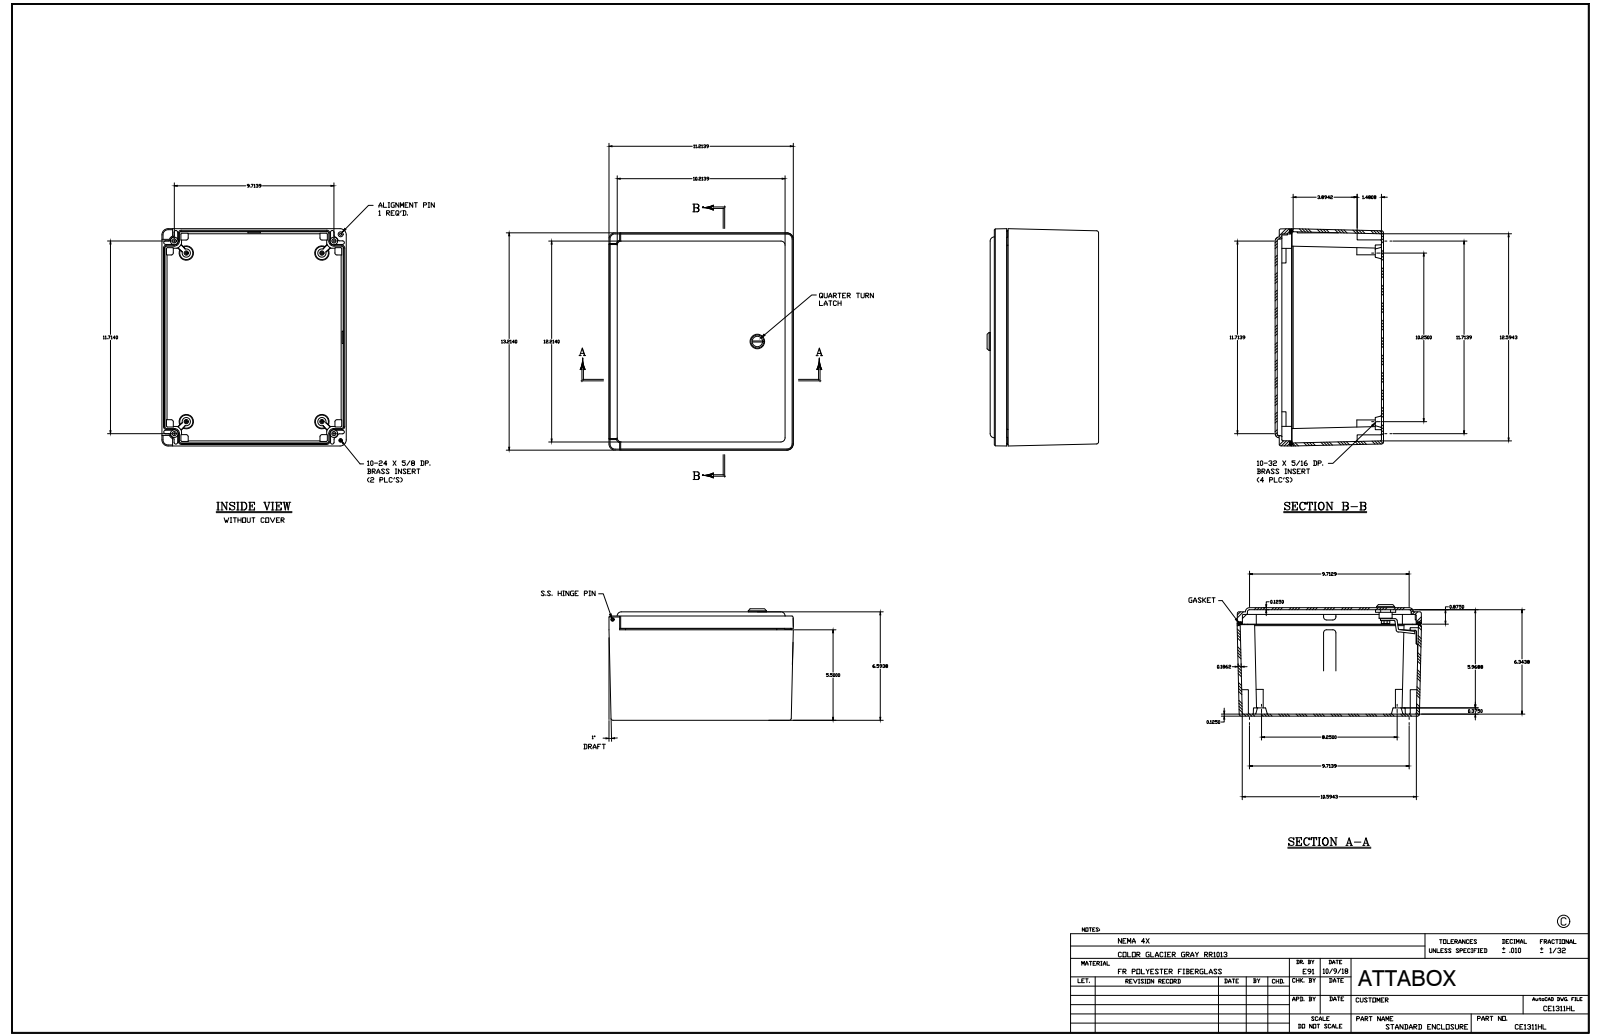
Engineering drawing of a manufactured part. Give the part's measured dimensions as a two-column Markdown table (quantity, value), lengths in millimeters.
| quantity | value |
| --- | --- |
| part name | CE1311HL |
| STEP written by | SolidWorks 2018 (AUTOMOTIVE_DESIGN) |
| units | millimeters |
| bodies | 27 solids, 1054 faces (430 planar, 313 cylindrical, 311 other) |
| overall size | 335.8 × 285.1 × 172.2 |
| volume | 1 803 000 mm³ |
| surface area | 844 500 mm² |
| round holes (diameter × count) | 7.1 × 6, 4 × 4, 8 × 4, 13.5 × 4, 2.4 × 2, 2.6 × 2, 3.3 × 2, 3.6 × 2, 3.7 × 2, 4 × 2, 5.6 × 2, 5.8 × 2 |
| round bosses / shafts (diameter × count) | 9.5 × 2, 5.9 × 2, 4.5 × 2, 2.4 × 2, 2.2 × 2, 27.8 × 1, 16 × 1, 10.2 × 1 |
| partial cylindrical surfaces (radius × count) | 0.8 × 60, 3.2 × 38, 1.6 × 26, 8 × 11, 1.5 × 8, 4.8 × 8, 6.4 × 8, 9.5 × 8 |
| main face-to-face distances | 3.2, 164.3, 4.7, 167.5, 161.1, 3.2, 6.4, 161.1, 158, 19.1 |
| hole center spacings | 26.4, 166, 229, 279.6, 290.8, 308.1, 318.3, 360.4 |
